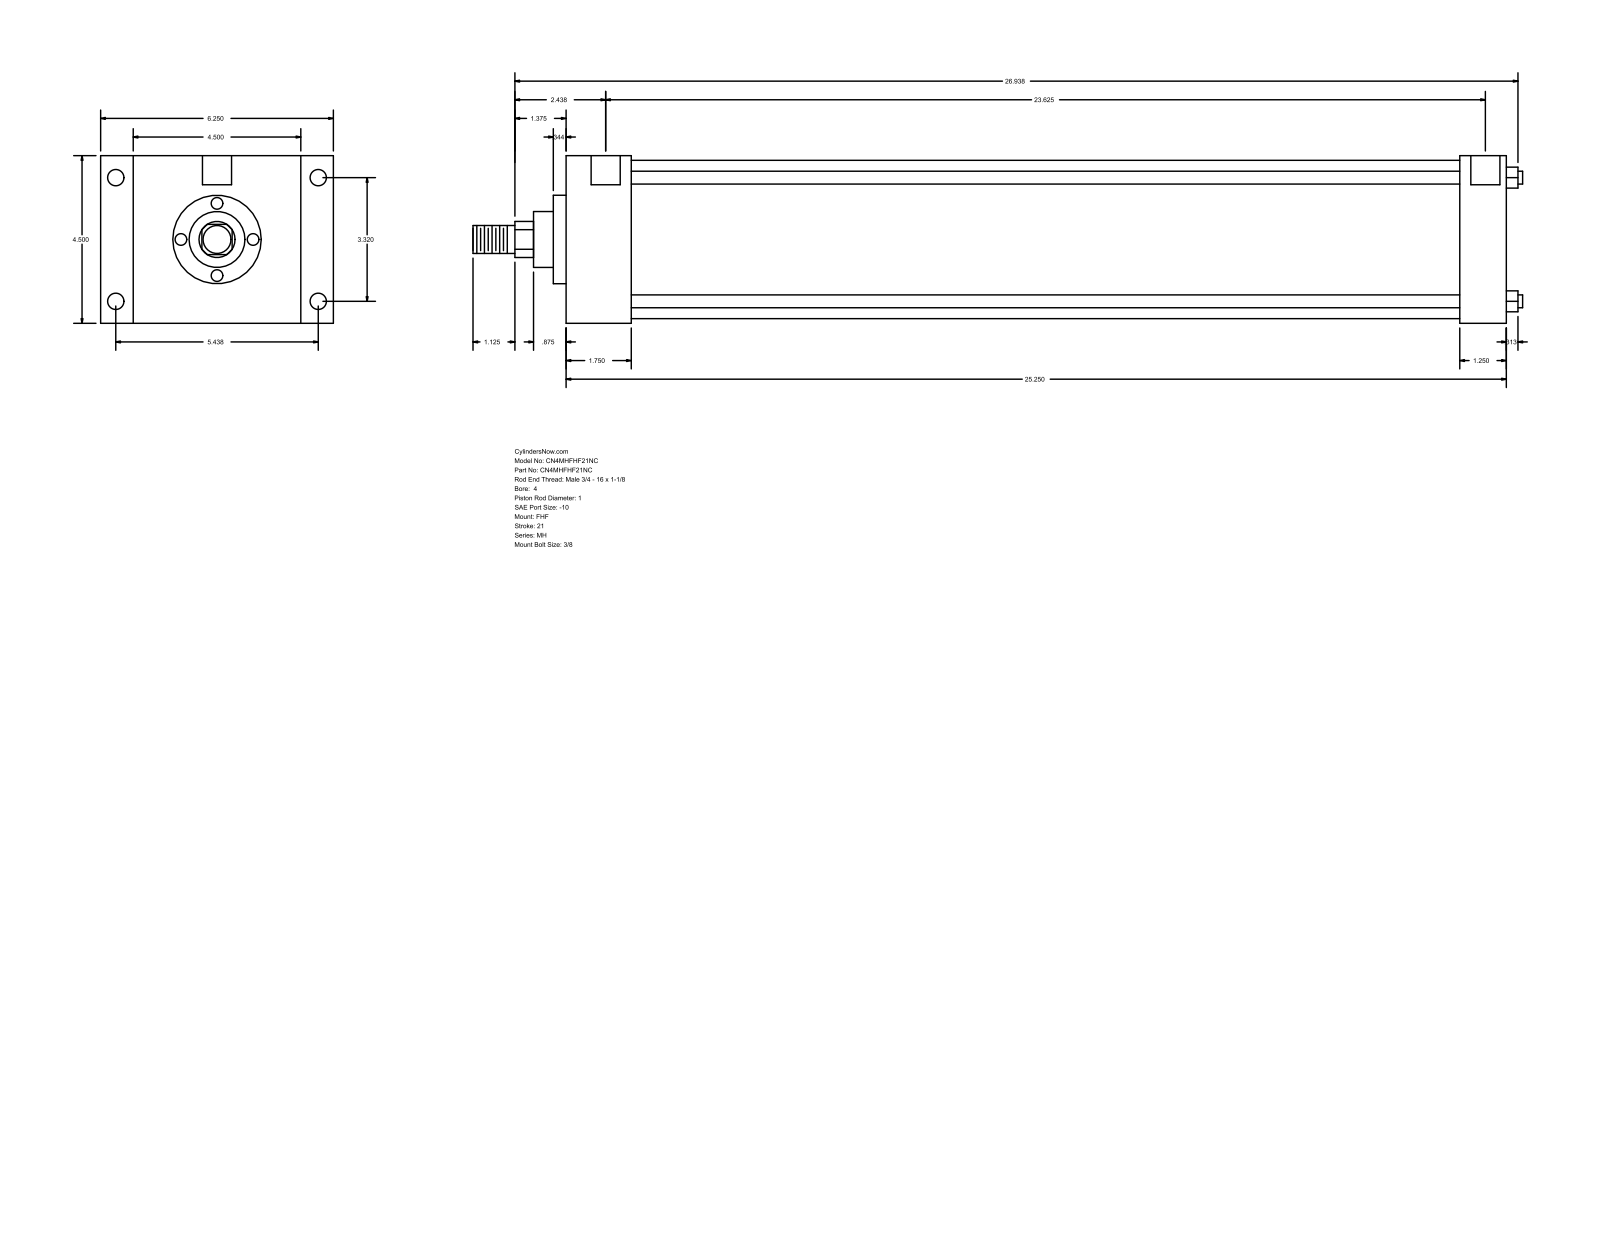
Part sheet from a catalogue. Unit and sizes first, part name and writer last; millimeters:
Units: millimetres
Overall size (bounding box): 715.96 × 158.75 × 114.3
Round holes (diameter × count): ⌀8.73 ×4, ⌀11.13 ×4, ⌀19.84 ×2
Round bosses / shafts (diameter × count): ⌀8.76 ×4, ⌀107.95 ×1, ⌀60.33 ×1, ⌀38.1 ×1, ⌀25.4 ×1, ⌀19.05 ×1
Partial cylindrical surfaces — rounded edges, fillets, slot ends (radius × count): R12.29 ×1
Main face-to-face distances: 114.3, 641.35, 44.46, 596.89, 22.23, 136.53, 158.76, 609.6, 565.14, 31.75
Hole centre spacings: 84.32, 138.12, 161.82, 603.25, 1.58, 1.59, 600.08, 601.66
Bodies: 0 solids, 90 faces (61 planar, 29 cylindrical, 0 other)
Part name (STEP PRODUCT): MH_FHF__0400_1
STEP written by: GSSL Pune (CONFIG_CONTROL_DESIGN)
